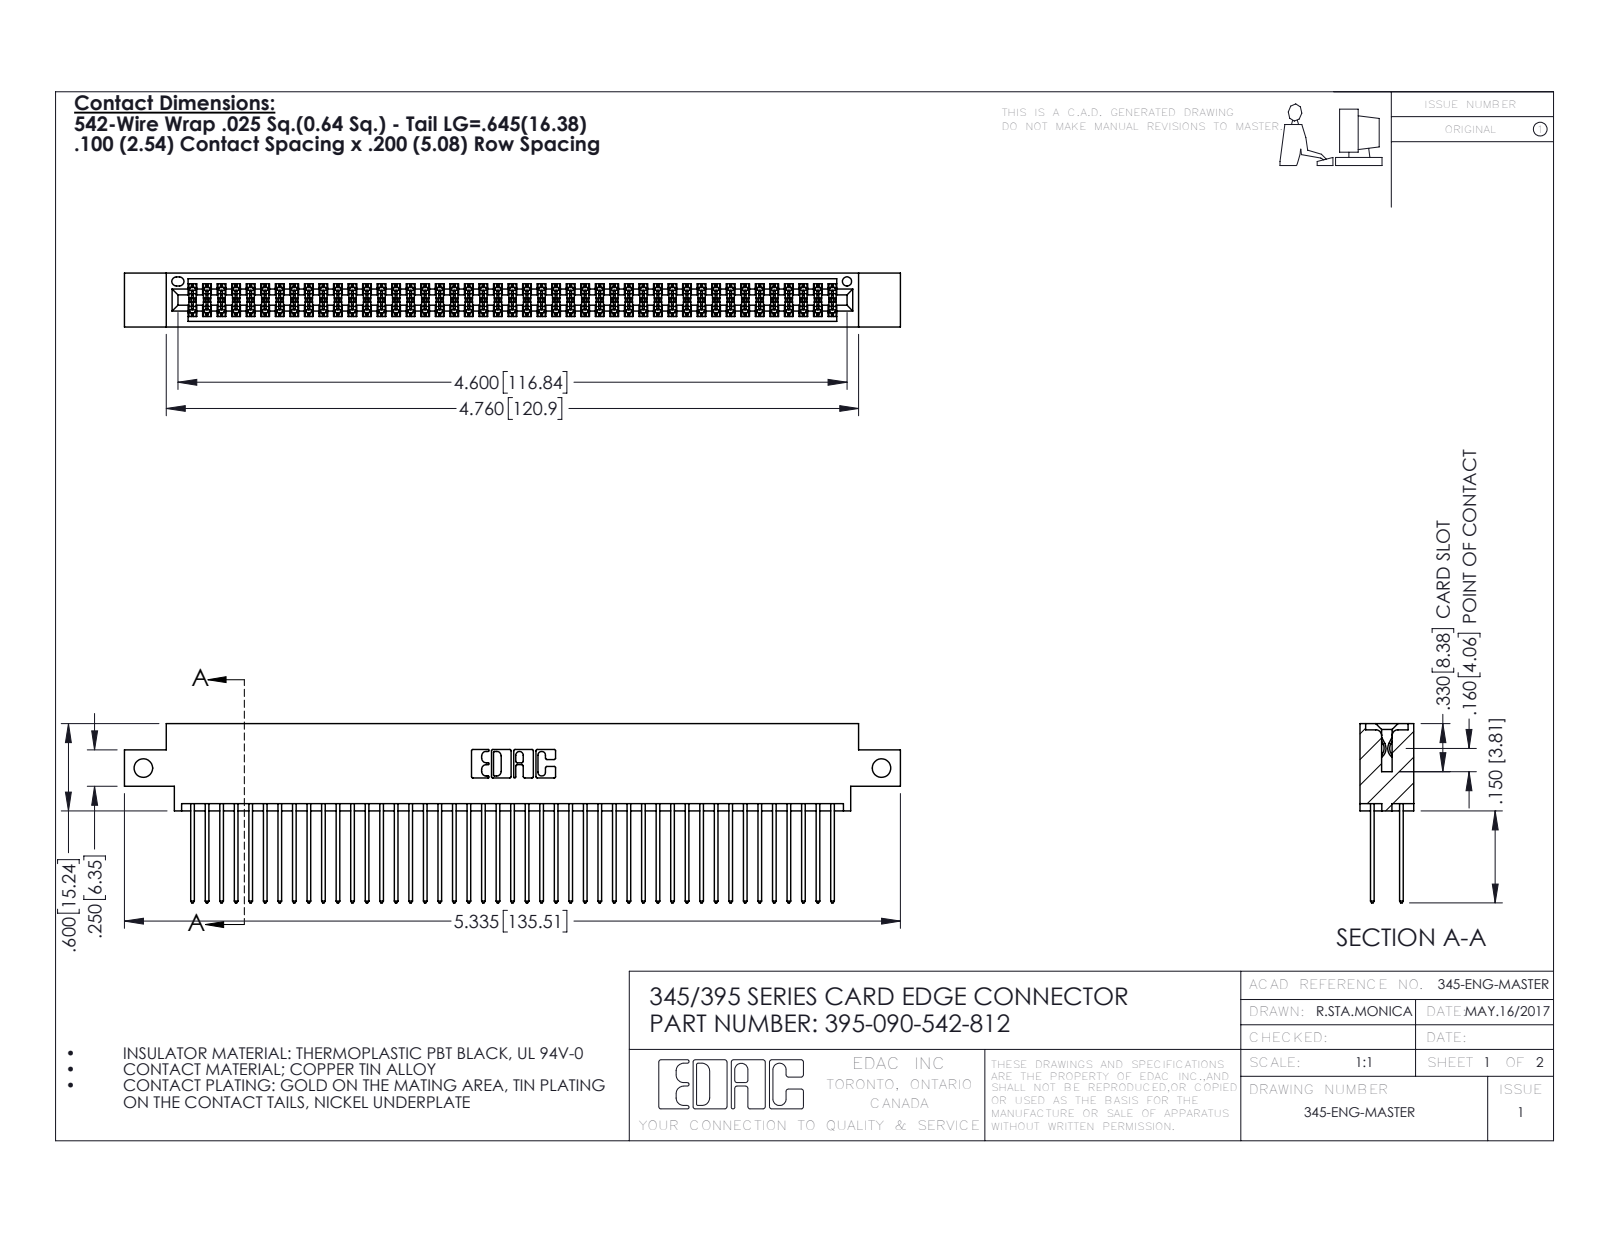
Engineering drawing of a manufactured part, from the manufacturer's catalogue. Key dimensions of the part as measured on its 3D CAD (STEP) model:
Part name (STEP PRODUCT): 395-090-542-812; 345-292-001_345-293-142; 345 Part_0.170 Offset - Side Mount
STEP written by: SolidWorks 2016 (CONFIG_CONTROL_DESIGN)
Units: inches
Bodies: 91 solids, 4630 faces (3054 planar, 1576 cylindrical, 0 other)
Overall size (bounding box): 5.335 × 1.232 × 0.37
Volume: 0.818 in³ · Surface area: 33.87 in²
Round holes (diameter × count): ⌀0.128 ×2, ⌀0.064 ×1
Partial cylindrical surfaces — rounded edges, fillets, slot ends (radius × count): R0.006 ×135, R0.01 ×90, R0.01 ×22, R0.007 ×6, R0.031 ×6, R0.026 ×3, R0.014 ×2, R0.019 ×2
Main face-to-face distances: 0.298, 0.072, 0.2, 0.098, 0.272, 0.025, 0.37, 0.225, 0.175, 0.149
Hole centre spacings: 5.075
